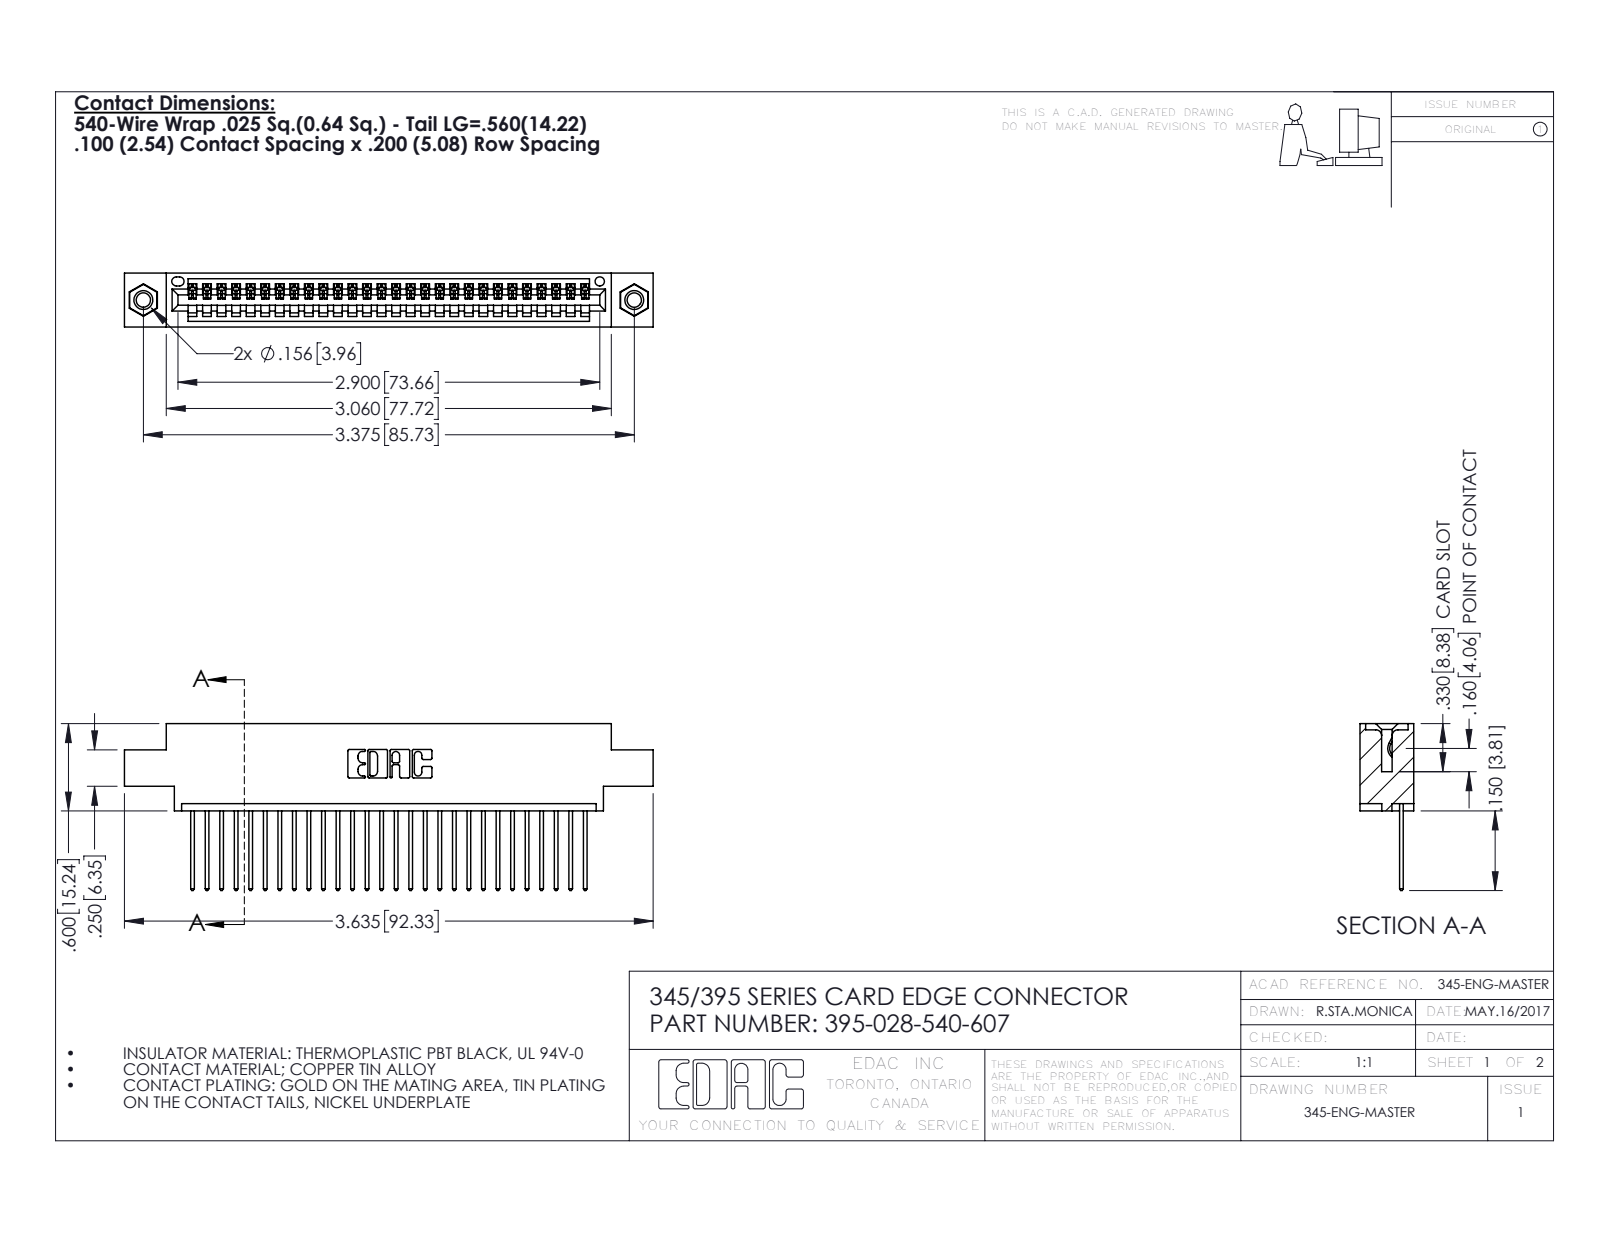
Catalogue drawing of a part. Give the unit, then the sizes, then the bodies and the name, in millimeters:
Units: millimetres
Overall size (bounding box): 92.3 × 29.1 × 9.4
Round holes (diameter × count): ⌀2.5 ×2, ⌀3.2 ×2, ⌀4 ×2, ⌀1.6 ×1
Round bosses / shafts (diameter × count): ⌀3.9 ×2
Partial cylindrical surfaces — rounded edges, fillets, slot ends (radius × count): R0.2 ×56, R0.3 ×56, R0.3 ×22, R0.2 ×6, R0.8 ×6, R0.7 ×3, R0.8 ×2, R1 ×2
Main face-to-face distances: 1.8, 7.6, 9.4, 5.1, 2.5, 6.9, 0.6, 5.7, 4.4, 3.8
Hole centre spacings: 6.9, 79.8, 85.7
Volume: 8 570 mm³ · Surface area: 11 630 mm²
Bodies: 31 solids, 1814 faces (1236 planar, 562 cylindrical, 16 other)
Part name (STEP PRODUCT): 345-250-001_345-250-005-103; 395-028-540-607; 345 Part_0.170 Offset - 0.156 Dia-TI; 345-292-001_345-293-140
STEP written by: SolidWorks 2016 (CONFIG_CONTROL_DESIGN)
